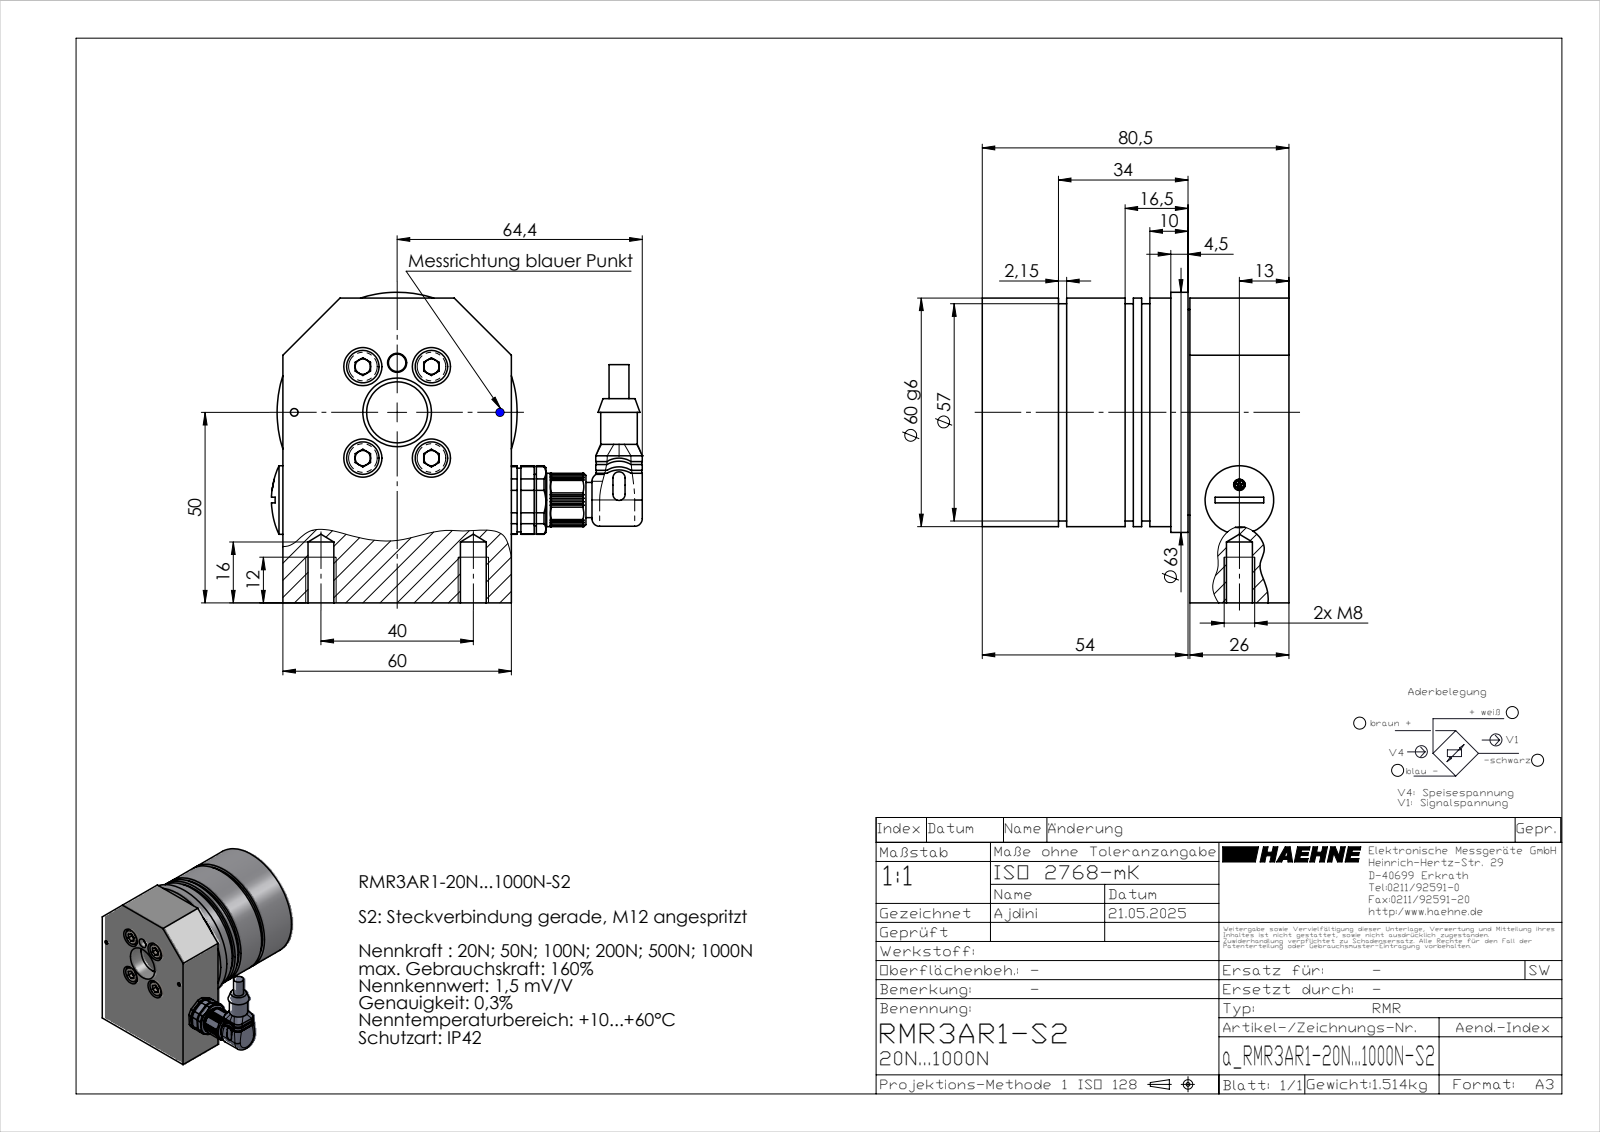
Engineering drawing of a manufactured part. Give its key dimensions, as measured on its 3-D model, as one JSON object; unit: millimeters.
{"part_name": "a_RMR3AR1-20N...1000N-S2", "step_written_by": "SolidWorks 2023 (AUTOMOTIVE_DESIGN)", "units": "millimeters", "bodies": {"solids": 15, "faces": 974, "planar": 533, "cylindrical": 248, "other": 193}, "overall_size": [97.34, 81.5, 80.5], "volume_mm3": 235738, "surface_area_mm2": 73396, "round_holes": [[1.1, 4], [1.15, 4], [1.6, 4], [1.85, 4], [4.2, 4], [5.3, 4], [10, 4], [2, 2], [6.8, 2], [0.64, 1], [1.2, 1], [3, 1]], "round_bosses_or_shafts": [[0.86, 5], [8.5, 4], [5, 4], [1.8, 4], [1.55, 4], [1.5, 4], [1, 4], [63, 1]], "partial_cylinders_radius": [[0.2, 16], [0.3, 9], [0.4, 4], [0.53, 4], [1, 4], [1.27, 4], [6, 4], [1.6, 2]], "face_to_face_distances": [11.5, 48.5, 37, 73, 54.5, 62, 11, 47, 15, 26], "hole_center_spacings": [2.5, 3.54, 15, 21.63, 37.95, 5, 9.06, 18]}
